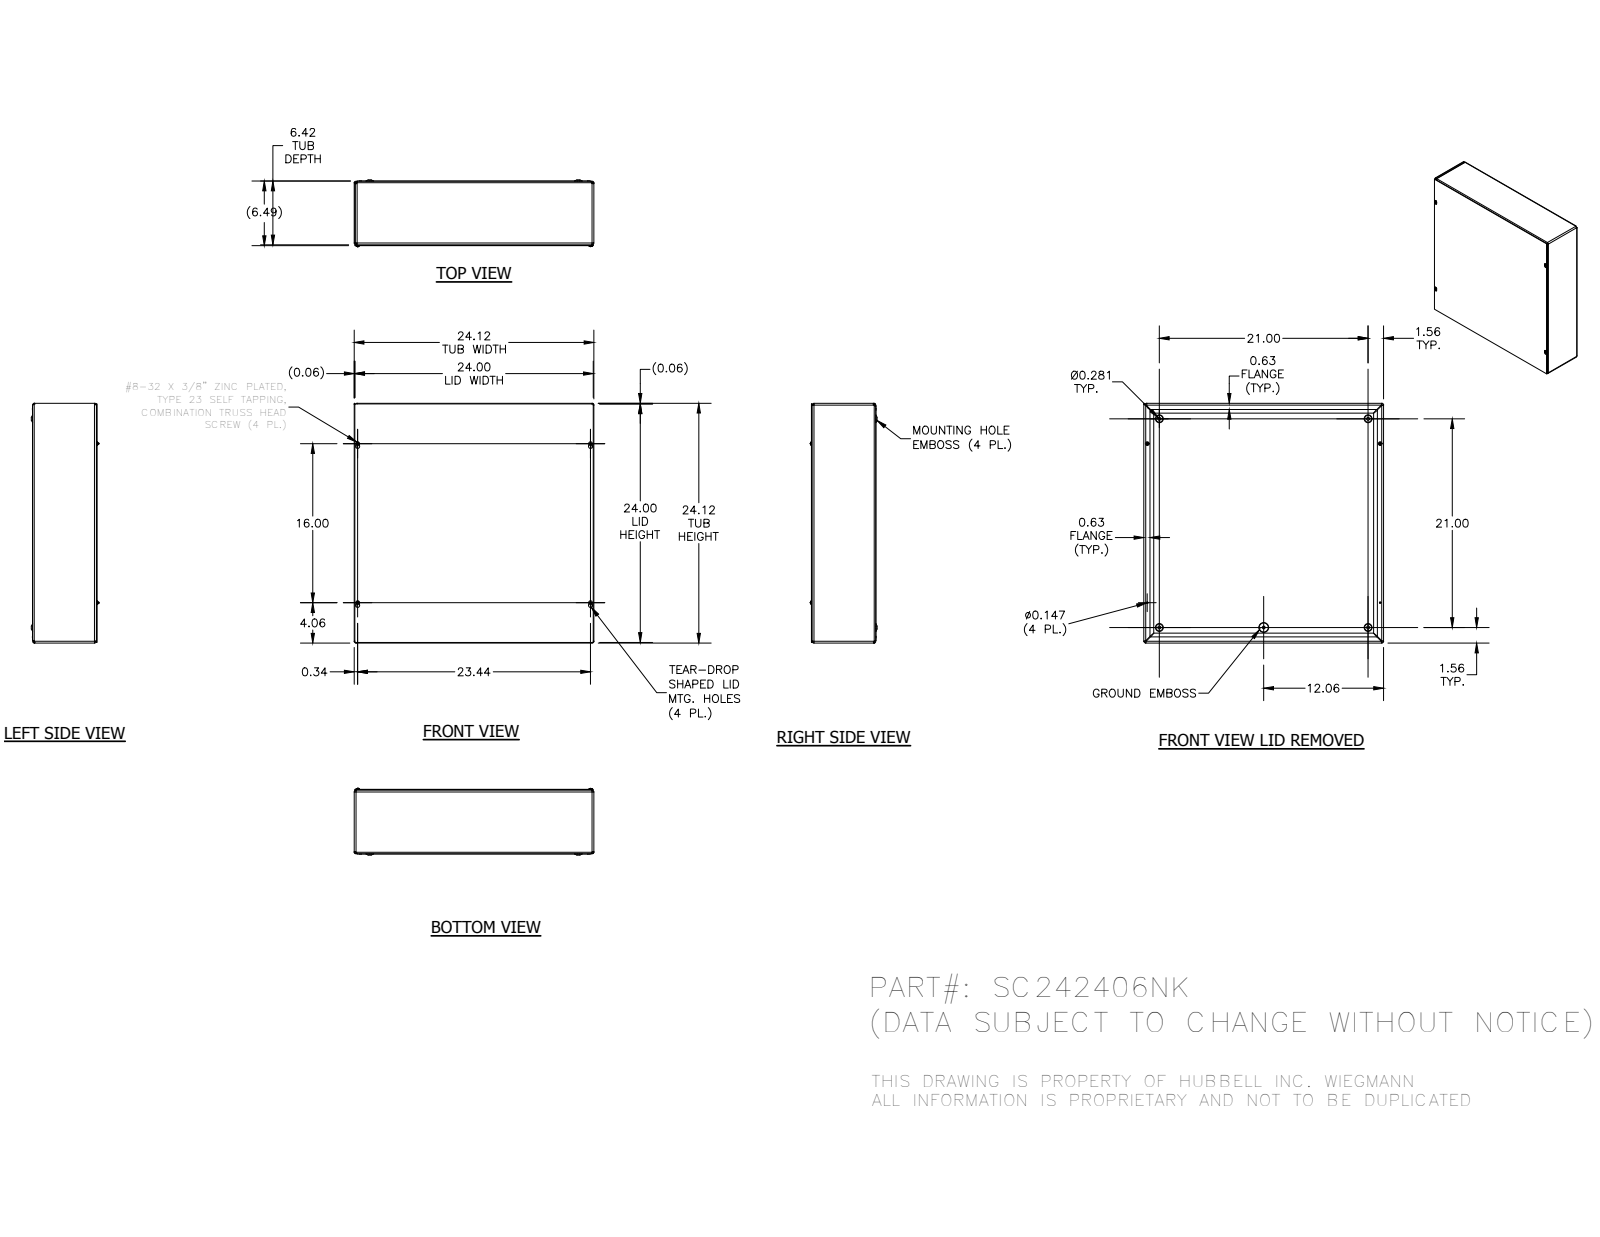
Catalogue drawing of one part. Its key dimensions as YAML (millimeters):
part_name: "SC2424BKP; SC242406NKWRA; SC2424LID; 34056 (+1 more)"
step_written_by: "Autodesk Inventor 2014 (AUTOMOTIVE_DESIGN)"
units: millimeters
bodies: {solids: 7, faces: 358, planar: 133, cylindrical: 75, other: 150}
overall_size: [612.77, 612.77, 170.59]
volume: 2135000
surface_area: 2448000
round_holes:
  - {diameter: 3.73, count: 4}
  - {diameter: 7.62, count: 4}
  - {diameter: 4.19, count: 1}
round_bosses_or_shafts:
  - {diameter: 4.57, count: 8}
  - {diameter: 9.75, count: 4}
  - {diameter: 4.17, count: 4}
  - {diameter: 5.8, count: 1}
partial_cylinders:
  - {radius: 3.17, count: 12}
  - {radius: 4.75, count: 8}
  - {radius: 1.4, count: 4}
  - {radius: 1.57, count: 4}
  - {radius: 2.38, count: 4}
  - {radius: 2.97, count: 4}
  - {radius: 3.15, count: 4}
  - {radius: 3.96, count: 4}
face_to_face_distances: [1.88, 163, 1.57, 161.12, 611.2, 164.88, 612.77, 609.63, 3.45, 159.55]
hole_center_spacings: [470.92, 533.4, 70.64, 70.65, 266.7, 406.4, 556.24, 567.91]
